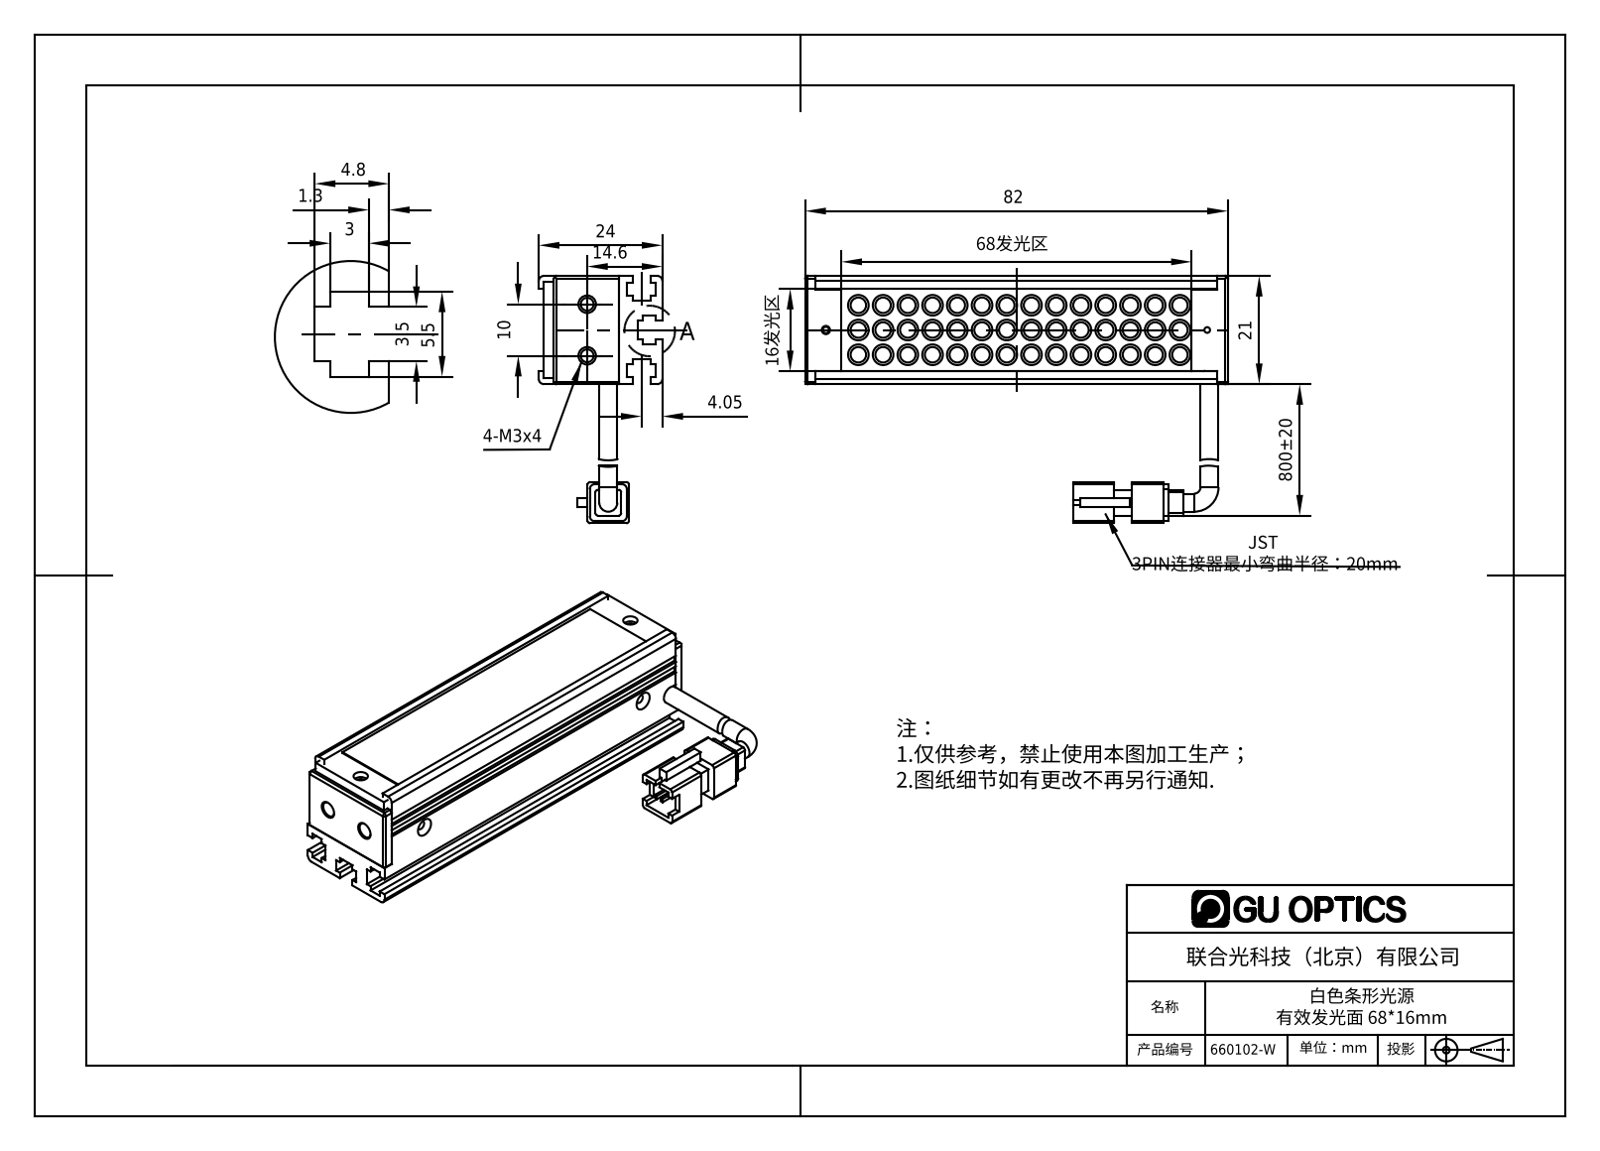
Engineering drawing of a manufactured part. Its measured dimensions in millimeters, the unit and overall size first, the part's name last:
Units: millimetres
Overall size (bounding box): 82 × 48 × 24
Round holes (diameter × count): ⌀1.6 ×5, ⌀1.5 ×2, ⌀1.7 ×2, ⌀2.5 ×2, ⌀2.8 ×2, ⌀3 ×2, ⌀1.1 ×1, ⌀1.25 ×1, ⌀2 ×1
Round bosses / shafts (diameter × count): ⌀4 ×42, ⌀3 ×42, ⌀3.5 ×2
Partial cylindrical surfaces — rounded edges, fillets, slot ends (radius × count): R1 ×12, R0.5 ×8, R1.65 ×1
Main face-to-face distances: 2, 1, 2.5, 18.5, 14.6, 21, 1.3, 8.5, 3.5, 12.6
Hole centre spacings: 74, 7, 7.18, 8.84, 67.02, 67.22, 74.33, 10
Volume: 25 111 mm³ · Surface area: 27 701 mm²
Bodies: 8 solids, 690 faces (294 planar, 251 cylindrical, 145 other)
Part name (STEP PRODUCT): 660102-W
STEP written by: SolidWorks 2016 (AUTOMOTIVE_DESIGN)
